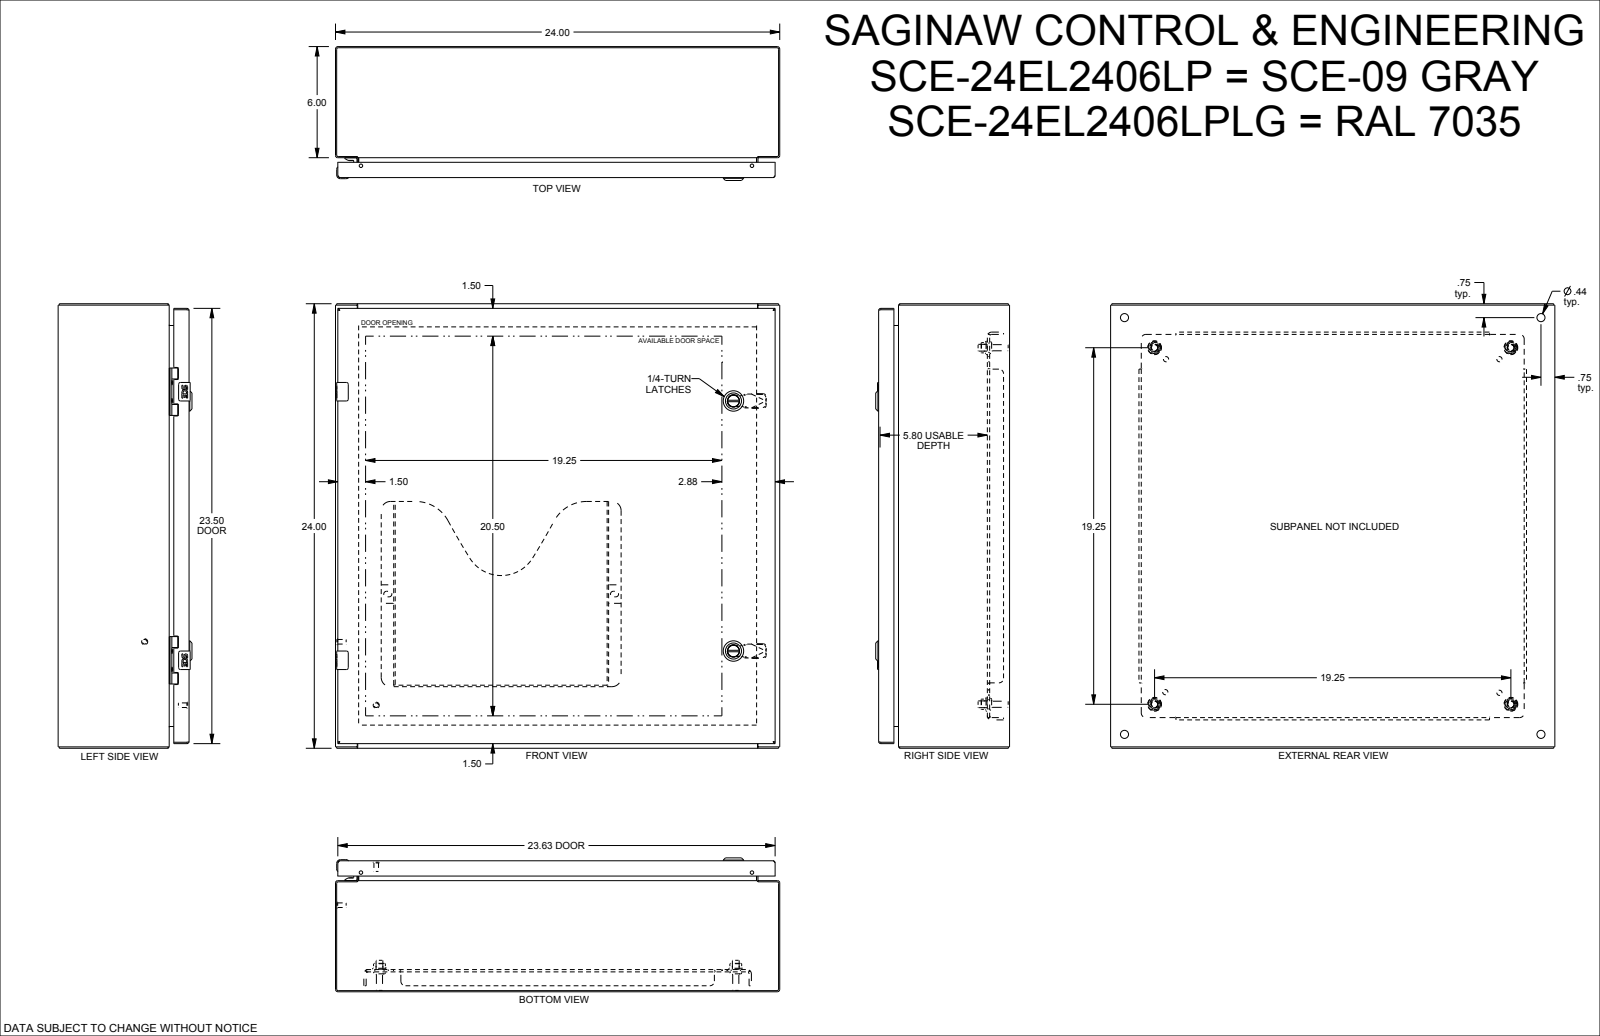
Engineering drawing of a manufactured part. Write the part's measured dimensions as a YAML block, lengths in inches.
part_name: "SCE-24EL2406LP"
step_written_by: "SolidWorks 2021 (AUTOMOTIVE_DESIGN)"
units: inches
bodies: {solids: 45, faces: 2819, planar: 1099, cylindrical: 850, other: 870}
overall_size: [24, 24, 7.23]
volume: 225.5
surface_area: 5388
round_holes:
  - {diameter: 0.172, count: 4}
  - {diameter: 0.205, count: 4}
  - {diameter: 0.244, count: 4}
  - {diameter: 0.266, count: 4}
  - {diameter: 0.281, count: 4}
  - {diameter: 0.367, count: 4}
  - {diameter: 0.375, count: 4}
  - {diameter: 0.437, count: 4}
  - {diameter: 0.5, count: 4}
  - {diameter: 0.04, count: 2}
  - {diameter: 0.188, count: 2}
  - {diameter: 0.197, count: 2}
round_bosses_or_shafts:
  - {diameter: 0.17, count: 6}
  - {diameter: 0.366, count: 4}
  - {diameter: 0.332, count: 4}
  - {diameter: 0.25, count: 4}
  - {diameter: 0.248, count: 4}
  - {diameter: 0.24, count: 4}
  - {diameter: 0.196, count: 3}
  - {diameter: 1.102, count: 2}
partial_cylinders:
  - {radius: 0.012, count: 56}
  - {radius: 0.01, count: 28}
  - {radius: 0.015, count: 24}
  - {radius: 0.02, count: 20}
  - {radius: 0.04, count: 17}
  - {radius: 0.06, count: 13}
  - {radius: 0.029, count: 12}
  - {radius: 0.1, count: 12}
face_to_face_distances: [0.075, 0.06, 23.925, 7.073, 6.998, 7.013, 6.938, 1.2, 5.873, 1]
hole_center_spacings: [20.938, 0.985, 14.5, 18.641, 20.38, 0.02, 0.493, 0.494]
